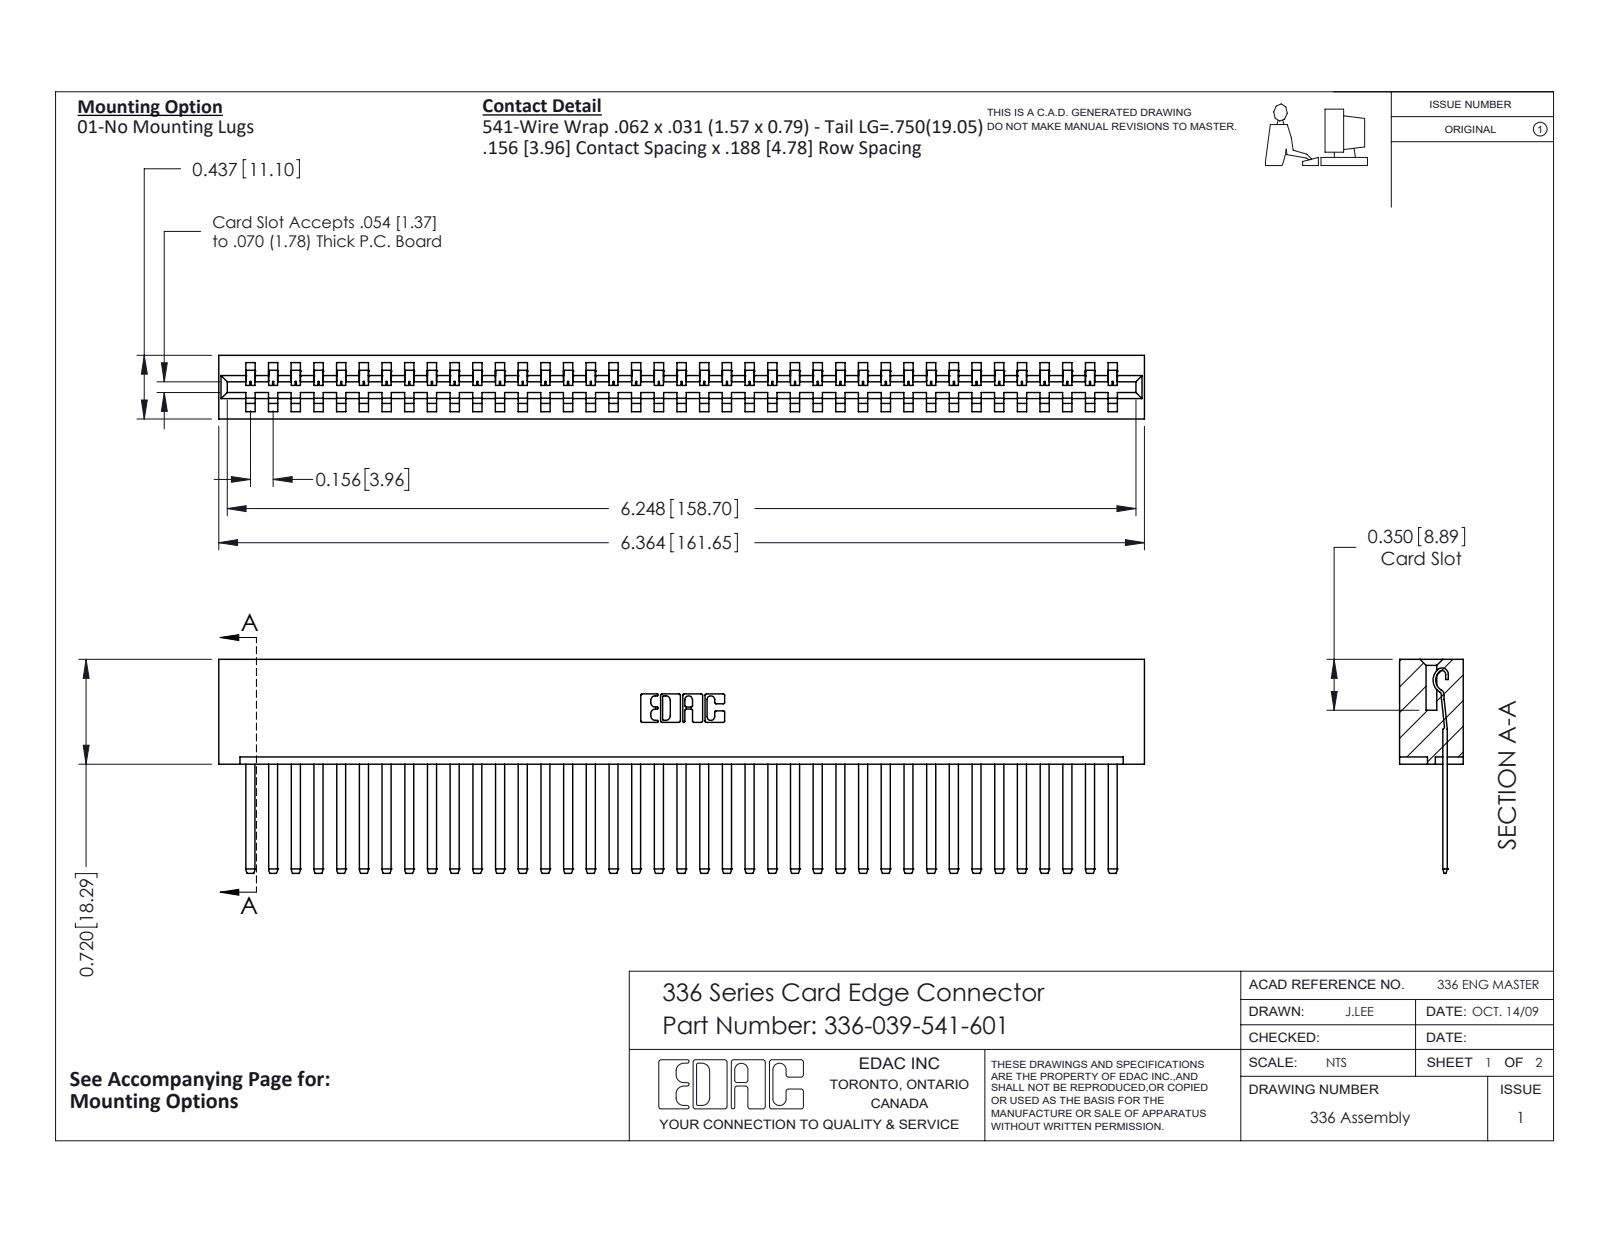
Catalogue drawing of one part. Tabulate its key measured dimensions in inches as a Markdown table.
| quantity | value |
| --- | --- |
| part name | 336-039-541-601; 336 Part_Lugless; 336-290-001_336-290-541 |
| STEP written by | SolidWorks 2020 (CONFIG_CONTROL_DESIGN) |
| units | inches |
| bodies | 40 solids, 2056 faces (1392 planar, 664 cylindrical, 0 other) |
| overall size | 6.364 × 1.47 × 0.437 |
| volume | 1.526 in³ |
| surface area | 42.17 in² |
| partial cylindrical surfaces (radius × count) | 0.004 × 78, 0.056 × 78, 0.01 × 22, 0.007 × 6, 0.031 × 6, 0.026 × 3, 0.022 × 2, 0.04 × 2 |
| main face-to-face distances | 0.437, 0.181, 0.328, 0.14, 0.297, 0.109, 0.031, 0.256, 0.05, 0.387 |
